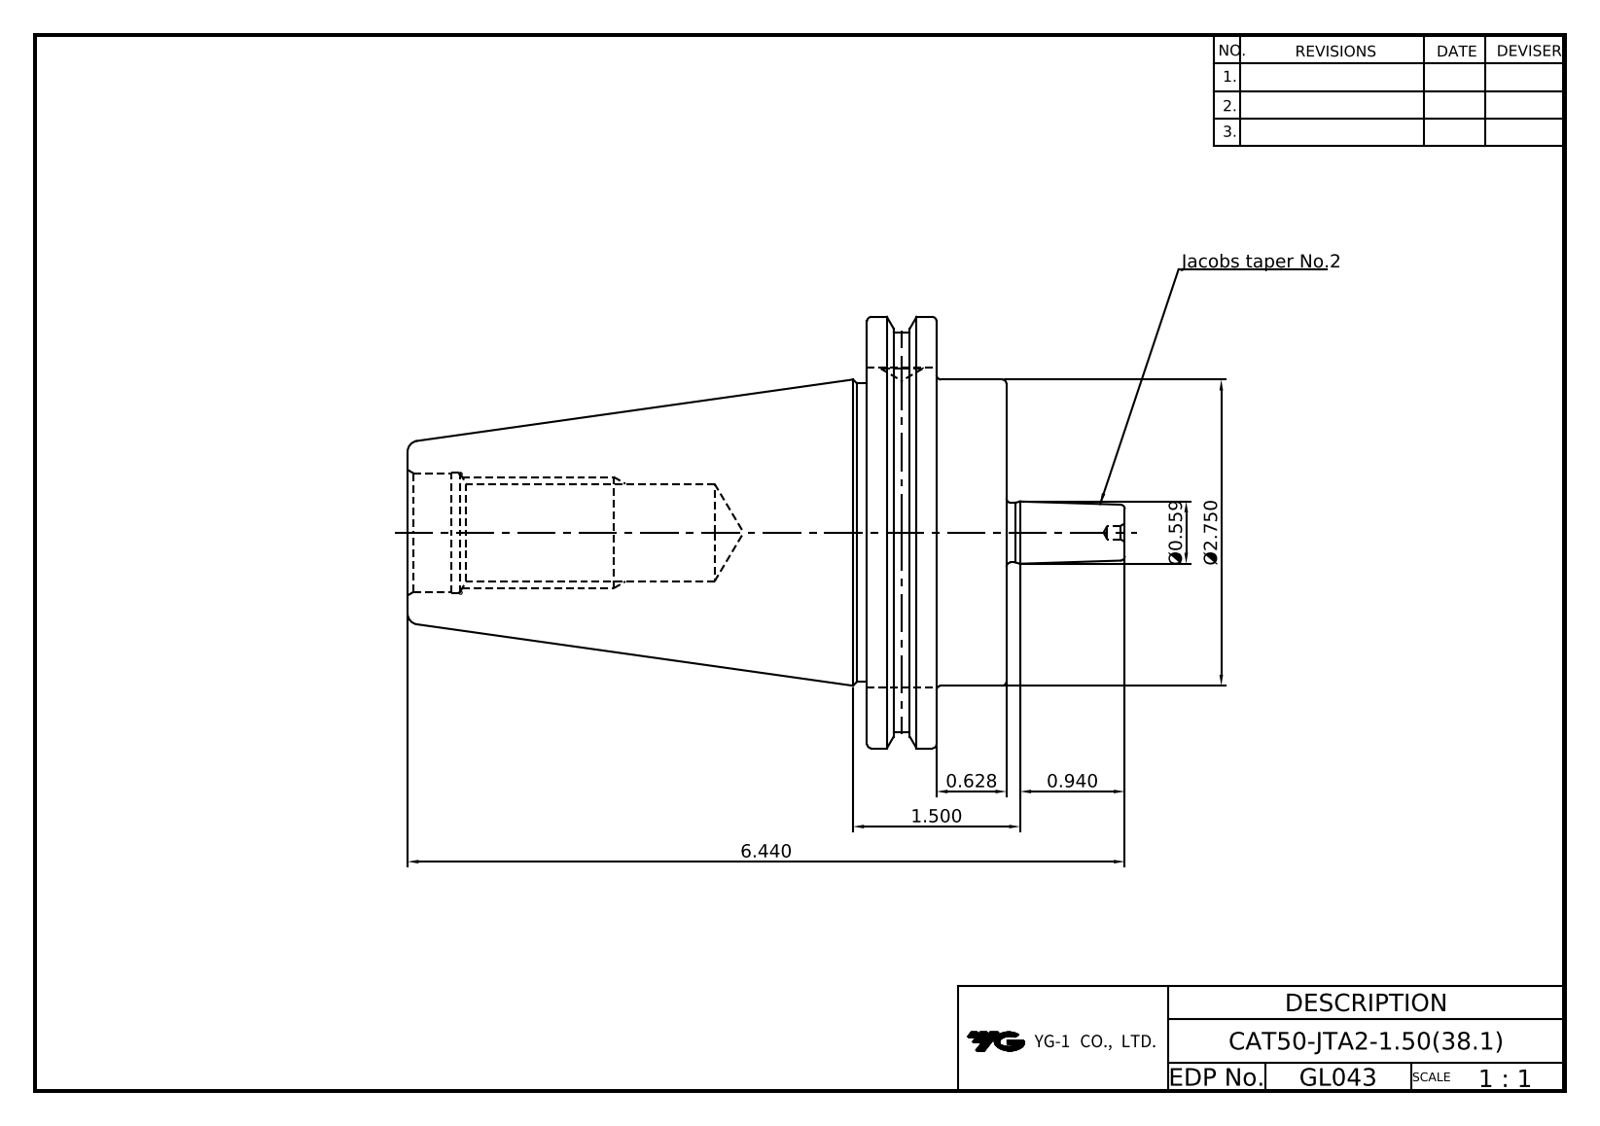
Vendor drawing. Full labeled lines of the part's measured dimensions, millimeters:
Part name (STEP PRODUCT): CAT50-JTA2-1.50(20231114)
STEP written by: Autodesk Inventor 2025 (AUTOMOTIVE_DESIGN)
Units: millimetres
Bodies: 1 solid, 60 faces (28 planar, 12 cylindrical, 20 other)
Overall size (bounding box): 163.58 × 98.42 × 94.69
Volume: 401 958 mm³ · Surface area: 45 558 mm²
Round holes (diameter × count): ⌀9.53 ×1, ⌀21.97 ×1, ⌀26.2 ×1
Round bosses / shafts (diameter × count): ⌀98.42 ×1, ⌀91.29 ×1, ⌀69.85 ×1, ⌀69.25 ×1, ⌀13.6 ×1
Main face-to-face distances: 15.95, 15.88, 31.83, 104.77, 120.65, 136.6, 73.03, 25.9, 114.64, 9.87
